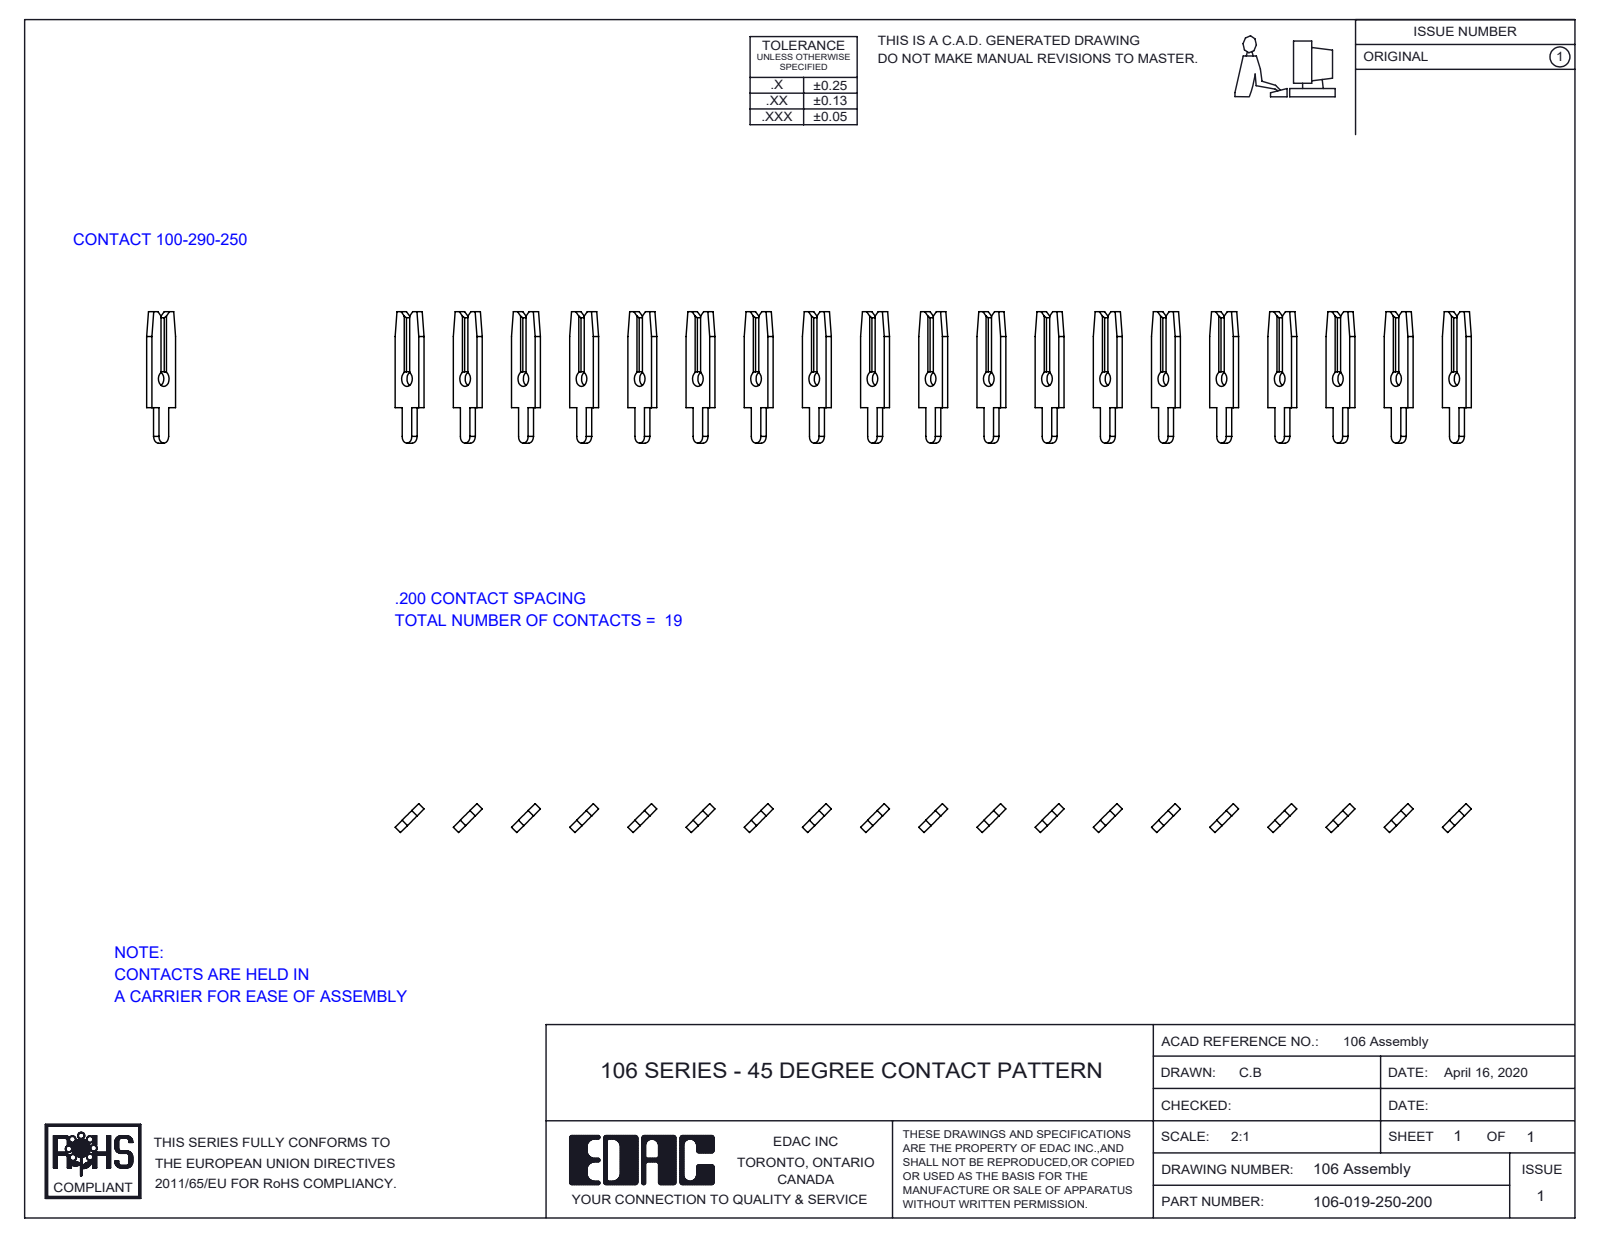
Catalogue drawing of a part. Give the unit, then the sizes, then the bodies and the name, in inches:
Units: inches
Overall size (bounding box): 3.7 × 0.452 × 0.1
Round holes (diameter × count): ⌀0.052 ×19
Partial cylindrical surfaces — rounded edges, fillets, slot ends (radius × count): R0.024 ×19
Main face-to-face distances: 0.141, 0.848, 0.283, 0.707, 0.99, 0.566, 0.424, 1.131, 0.424, 1.556
Hole centre spacings: 0.141, 0.283, 0.424, 0.848, 0.99, 1.131, 1.556, 0.566
Volume: 0.018 in³ · Surface area: 2.16 in²
Bodies: 19 solids, 456 faces (380 planar, 76 cylindrical, 0 other)
Part name (STEP PRODUCT): 100-290-001_100-290-250; 106-019-250-200
STEP written by: SolidWorks 2016 (CONFIG_CONTROL_DESIGN)
